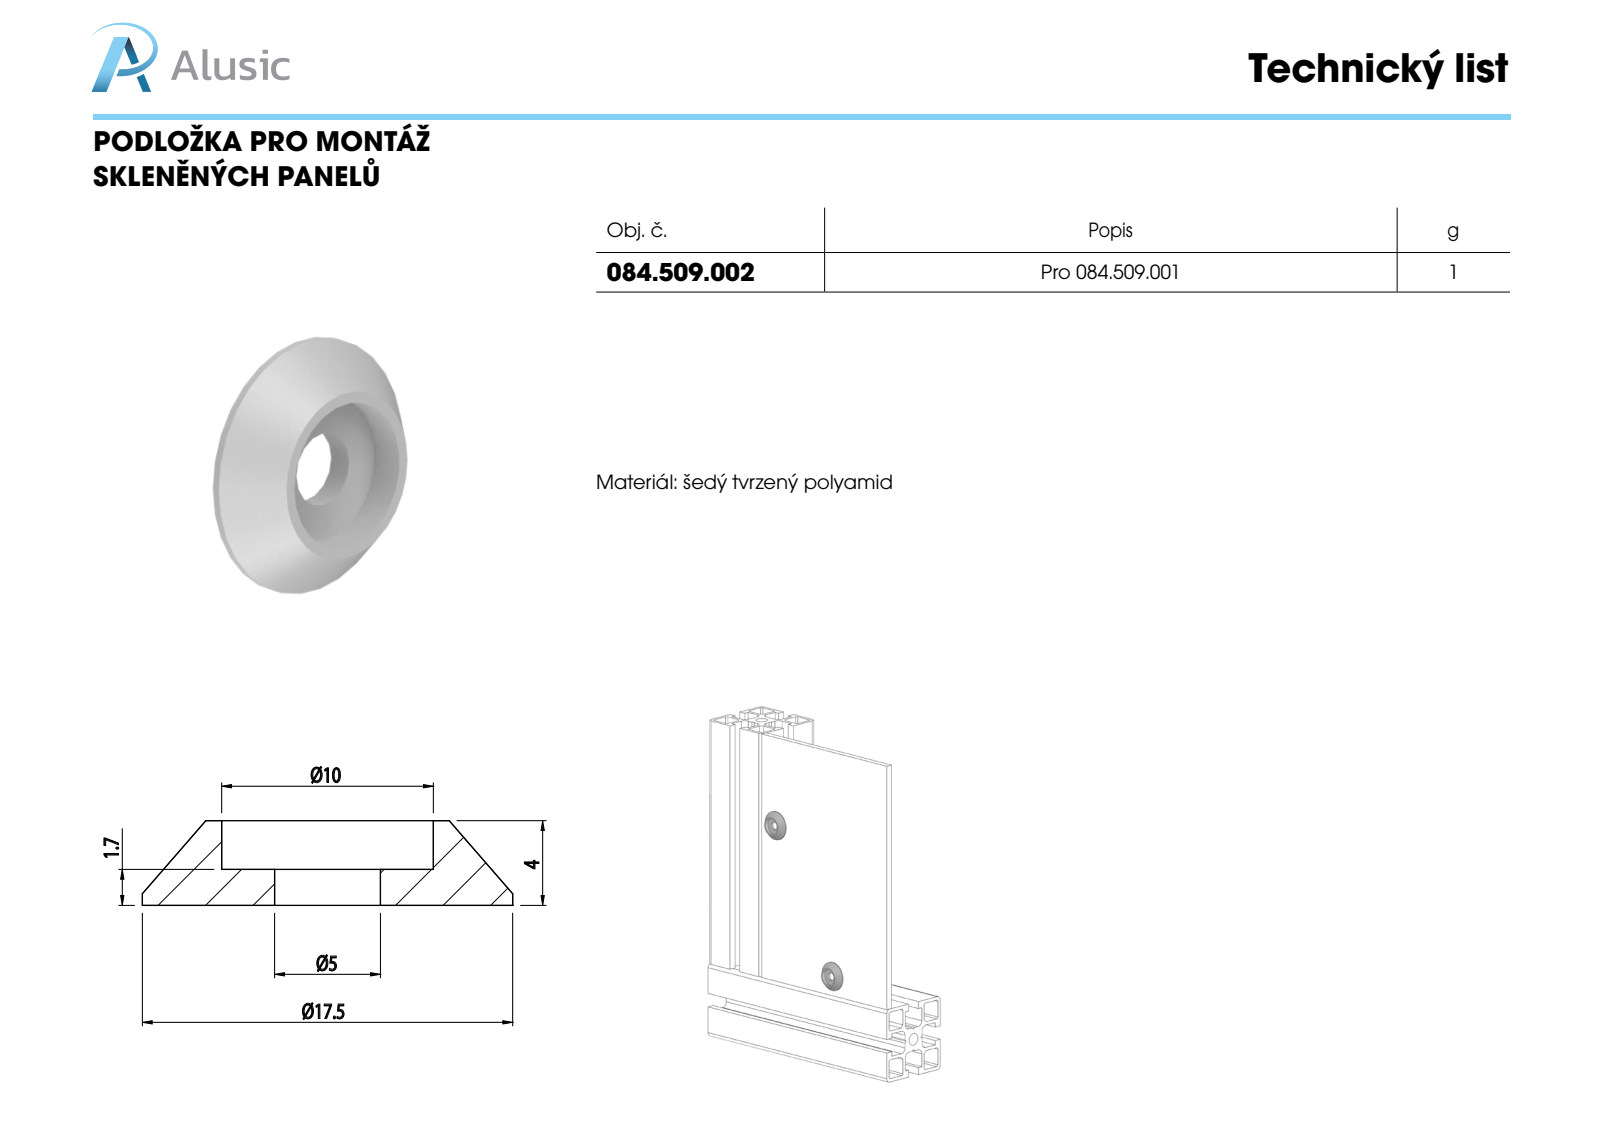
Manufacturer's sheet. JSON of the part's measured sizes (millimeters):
{"part_name": "084.509.002", "step_written_by": "SolidWorks 2011 (CONFIG_CONTROL_DESIGN)", "units": "millimeters", "bodies": {"solids": 1, "faces": 11, "planar": 3, "cylindrical": 6, "other": 2}, "overall_size": [17.5, 17.5, 4], "volume_mm3": 496, "surface_area_mm2": 643, "round_holes": [[5, 1], [10, 1]], "round_bosses_or_shafts": [[17.5, 1]], "face_to_face_distances": [1.7, 4, 2.3]}
